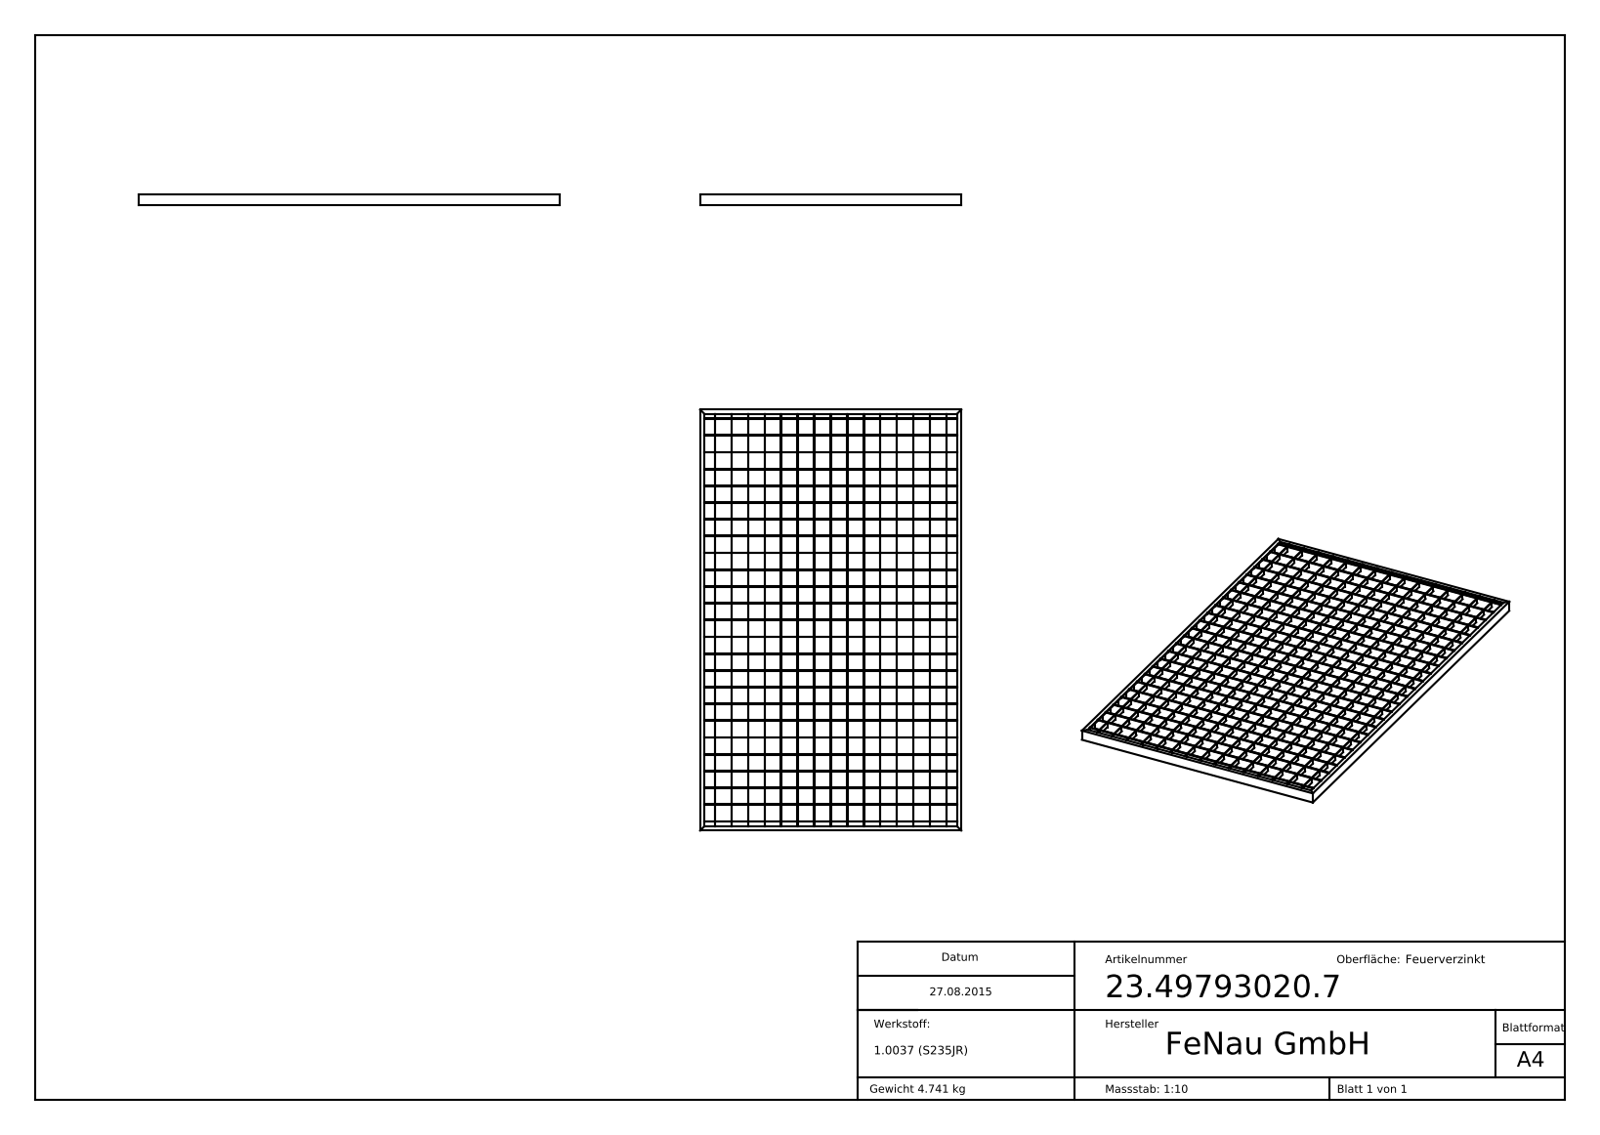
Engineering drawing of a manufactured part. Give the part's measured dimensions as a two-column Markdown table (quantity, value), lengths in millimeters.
| quantity | value |
| --- | --- |
| part name | 23-49793020-7 |
| STEP written by | SolidWorks 2015 (CONFIG_CONTROL_DESIGN) |
| units | millimeters |
| bodies | 1 solid, 1450 faces (1450 planar, 0 cylindrical, 0 other) |
| overall size | 790 × 490 × 20 |
| volume | 607 835 mm³ |
| surface area | 899 407 mm² |
| main face-to-face distances | 63, 31.5, 94.5, 31, 126, 157.5, 62, 189, 220.5, 252 |
